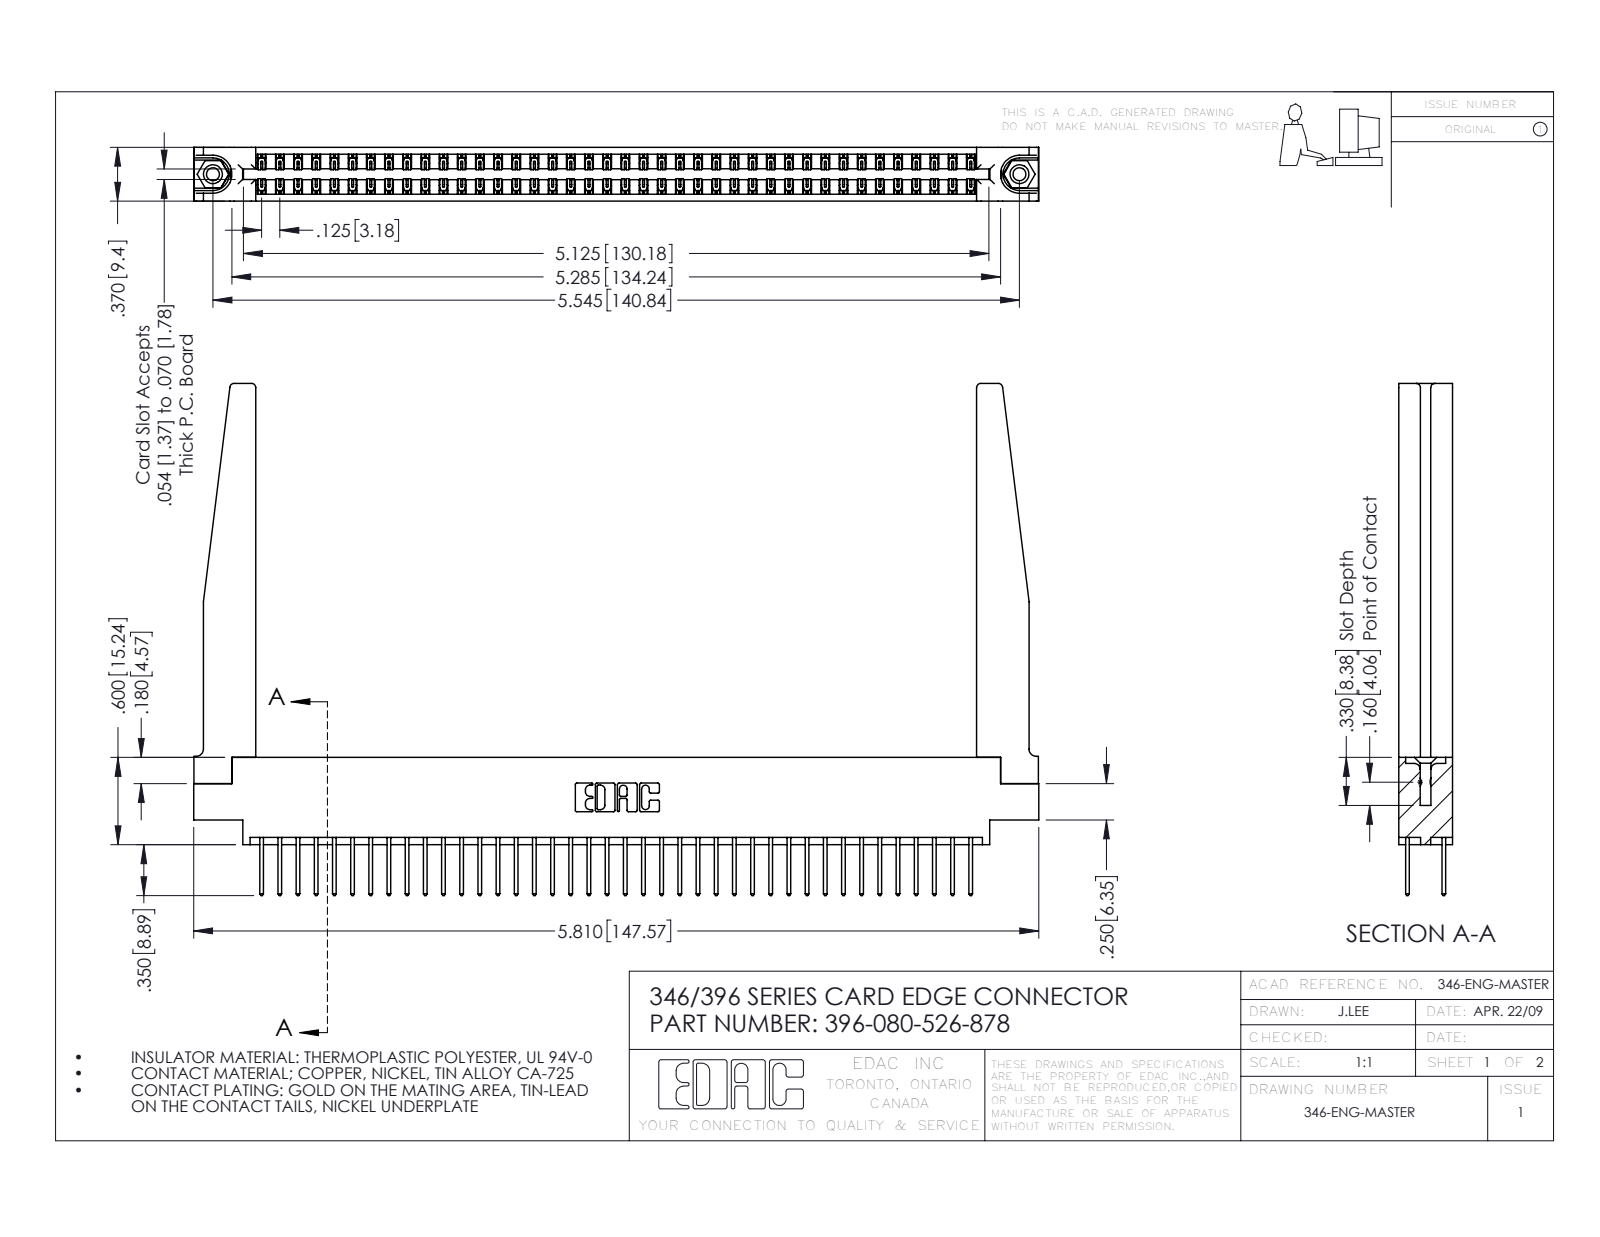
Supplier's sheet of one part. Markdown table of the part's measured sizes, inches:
| quantity | value |
| --- | --- |
| part name | 345-292-001_345-293-126; 346 Part_0.170 Offset - 0.156 Dia-TH; 345-250-001_345-250-001-102; 346-220-078_345-220-078 (+1 more) |
| STEP written by | SolidWorks 2016 (CONFIG_CONTROL_DESIGN) |
| units | inches |
| bodies | 85 solids, 4520 faces (3022 planar, 1446 cylindrical, 52 other) |
| overall size | 5.81 × 3.52 × 0.37 |
| volume | 1.297 in³ |
| surface area | 41.85 in² |
| round holes (diameter × count) | 0.089 × 2, 0.125 × 2, 0.156 × 2, 0.064 × 1 |
| round bosses / shafts (diameter × count) | 0.155 × 2 |
| partial cylindrical surfaces (radius × count) | 0.006 × 120, 0.01 × 80, 0.01 × 22, 0.03 × 8, 0.007 × 6, 0.031 × 6, 0.026 × 3, 0.014 × 2 |
| main face-to-face distances | 0.37, 0.048, 0.322, 0.072, 0.25, 0.298, 0.025, 0.148, 0.15, 0.275 |
| hole center spacings | 0.246, 5.336, 5.545 |
